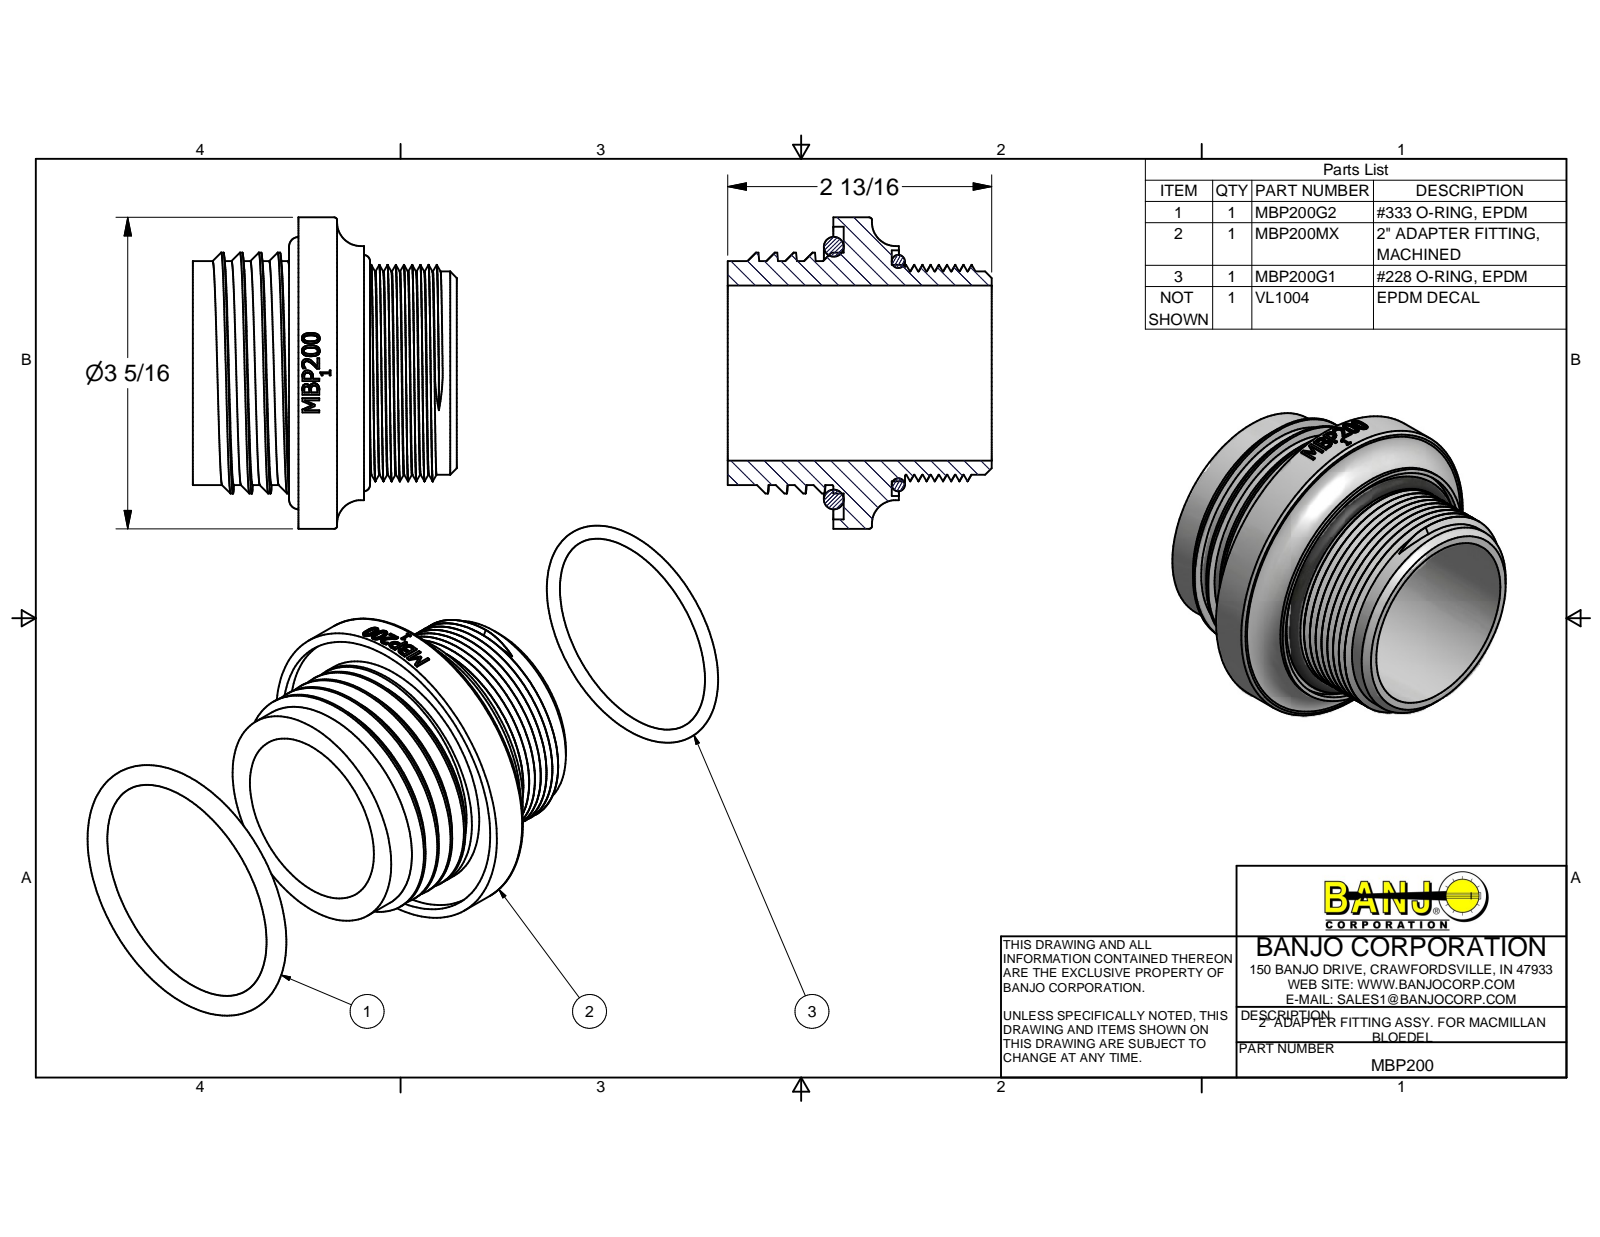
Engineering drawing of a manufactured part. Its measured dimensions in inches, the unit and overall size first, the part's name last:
Units: inches
Overall size (bounding box): 3.32 × 3.31 × 2.8
Round holes (diameter × count): ⌀1.86 ×1, ⌀2.61 ×1, ⌀3.11 ×1
Round bosses / shafts (diameter × count): ⌀3.31 ×1, ⌀2.7 ×1, ⌀2.56 ×1, ⌀2.38 ×1, ⌀2.3 ×1, ⌀2.16 ×1
Partial cylindrical surfaces — rounded edges, fillets, slot ends (radius × count): R0.61 ×1, R0.685 ×1, R1.665 ×1
Main face-to-face distances: 1.23, 1.12, 0.11, 1.74, 0.62, 0.51, 2.8, 1.68, 1.57, 1.06
Volume: 6.717 in³ · Surface area: 69.27 in²
Bodies: 3 solids, 174 faces (52 planar, 47 cylindrical, 75 other)
Part name (STEP PRODUCT): MBP200G2; MBP200X; MBP200MX; MBP200G1 (+1 more)
STEP written by: Autodesk Inventor 2014 (AUTOMOTIVE_DESIGN)
